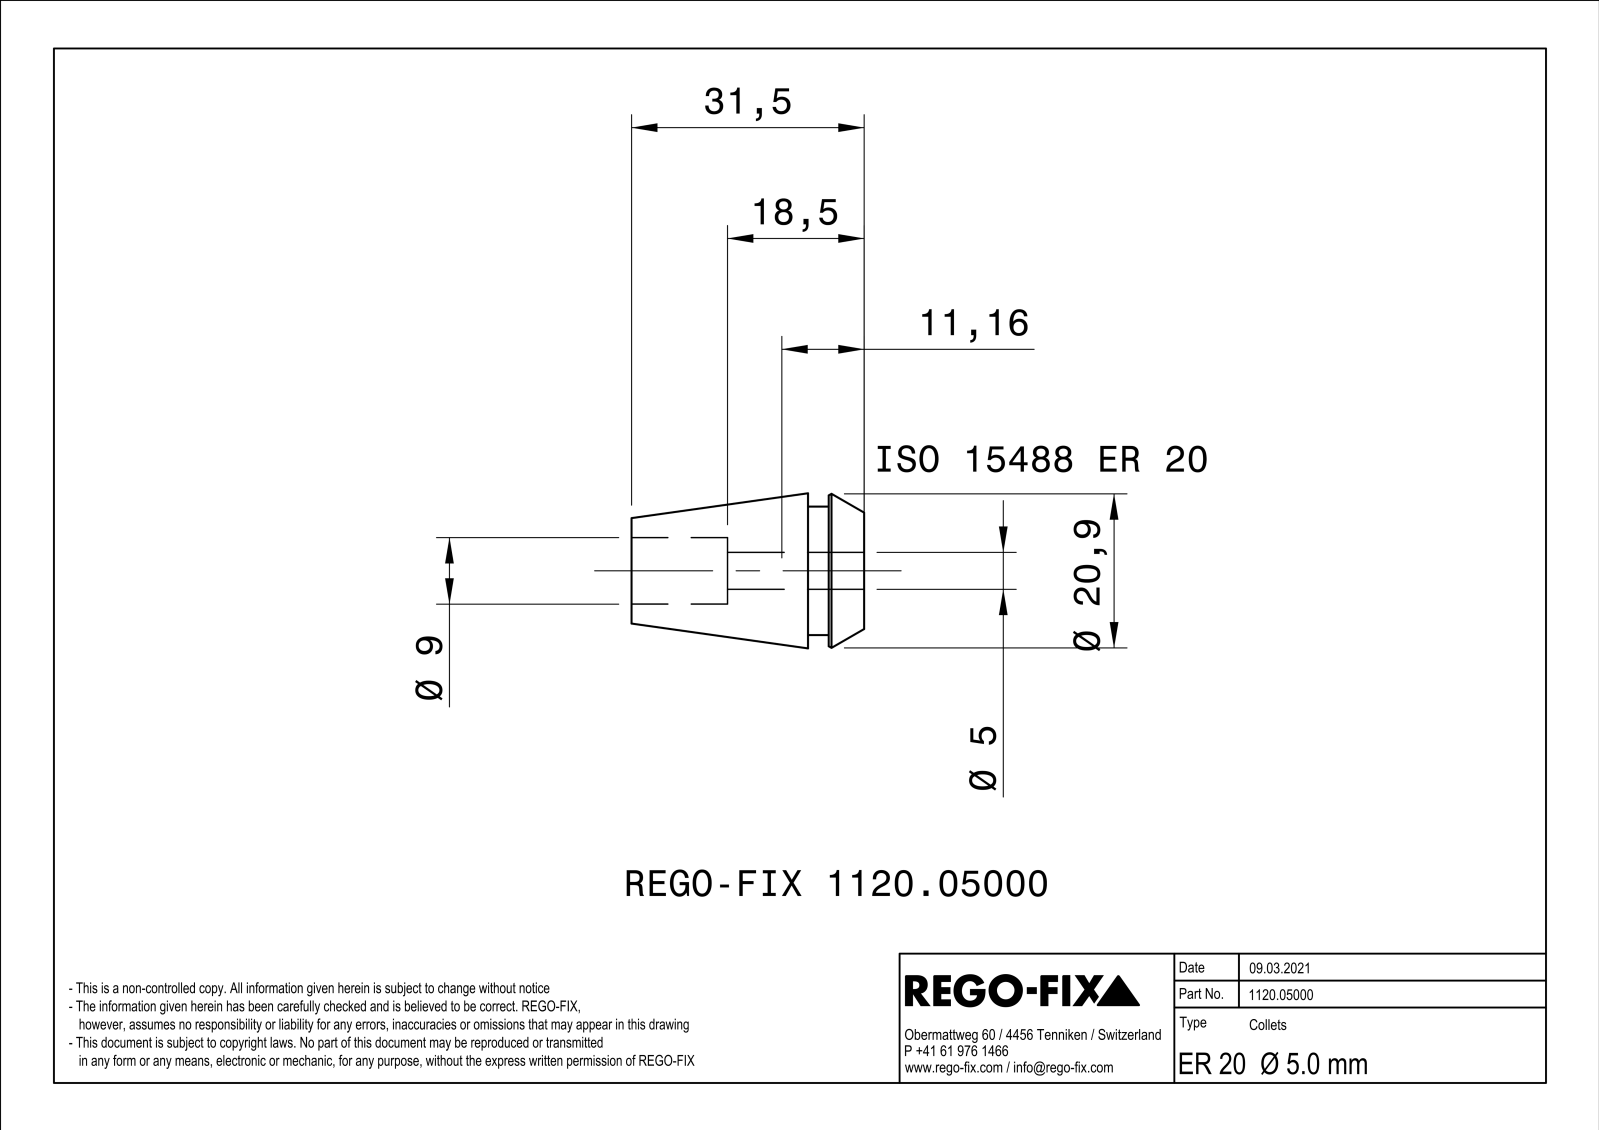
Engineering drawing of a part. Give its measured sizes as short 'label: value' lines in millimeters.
name: NOCUT
written by: SIEMENS PLM Software Solid Edge ST10 (AUTOMOTIVE_DESIGN)
unit: mm
bodies: 1 solid, 257 faces (104 planar, 41 cylindrical, 112 other)
size: 31.5 × 20.99 × 20.99
volume: 5 472 mm³; area: 6 537 mm²
holes: 1× ⌀9
bosses: 1× ⌀17.4
rounds: 8× R40, 1× R2.5
face distances: 0.6, 0.62, 0.58, 7.6, 4.8, 2.8, 31.5, 26.7, 23.9, 18.5
